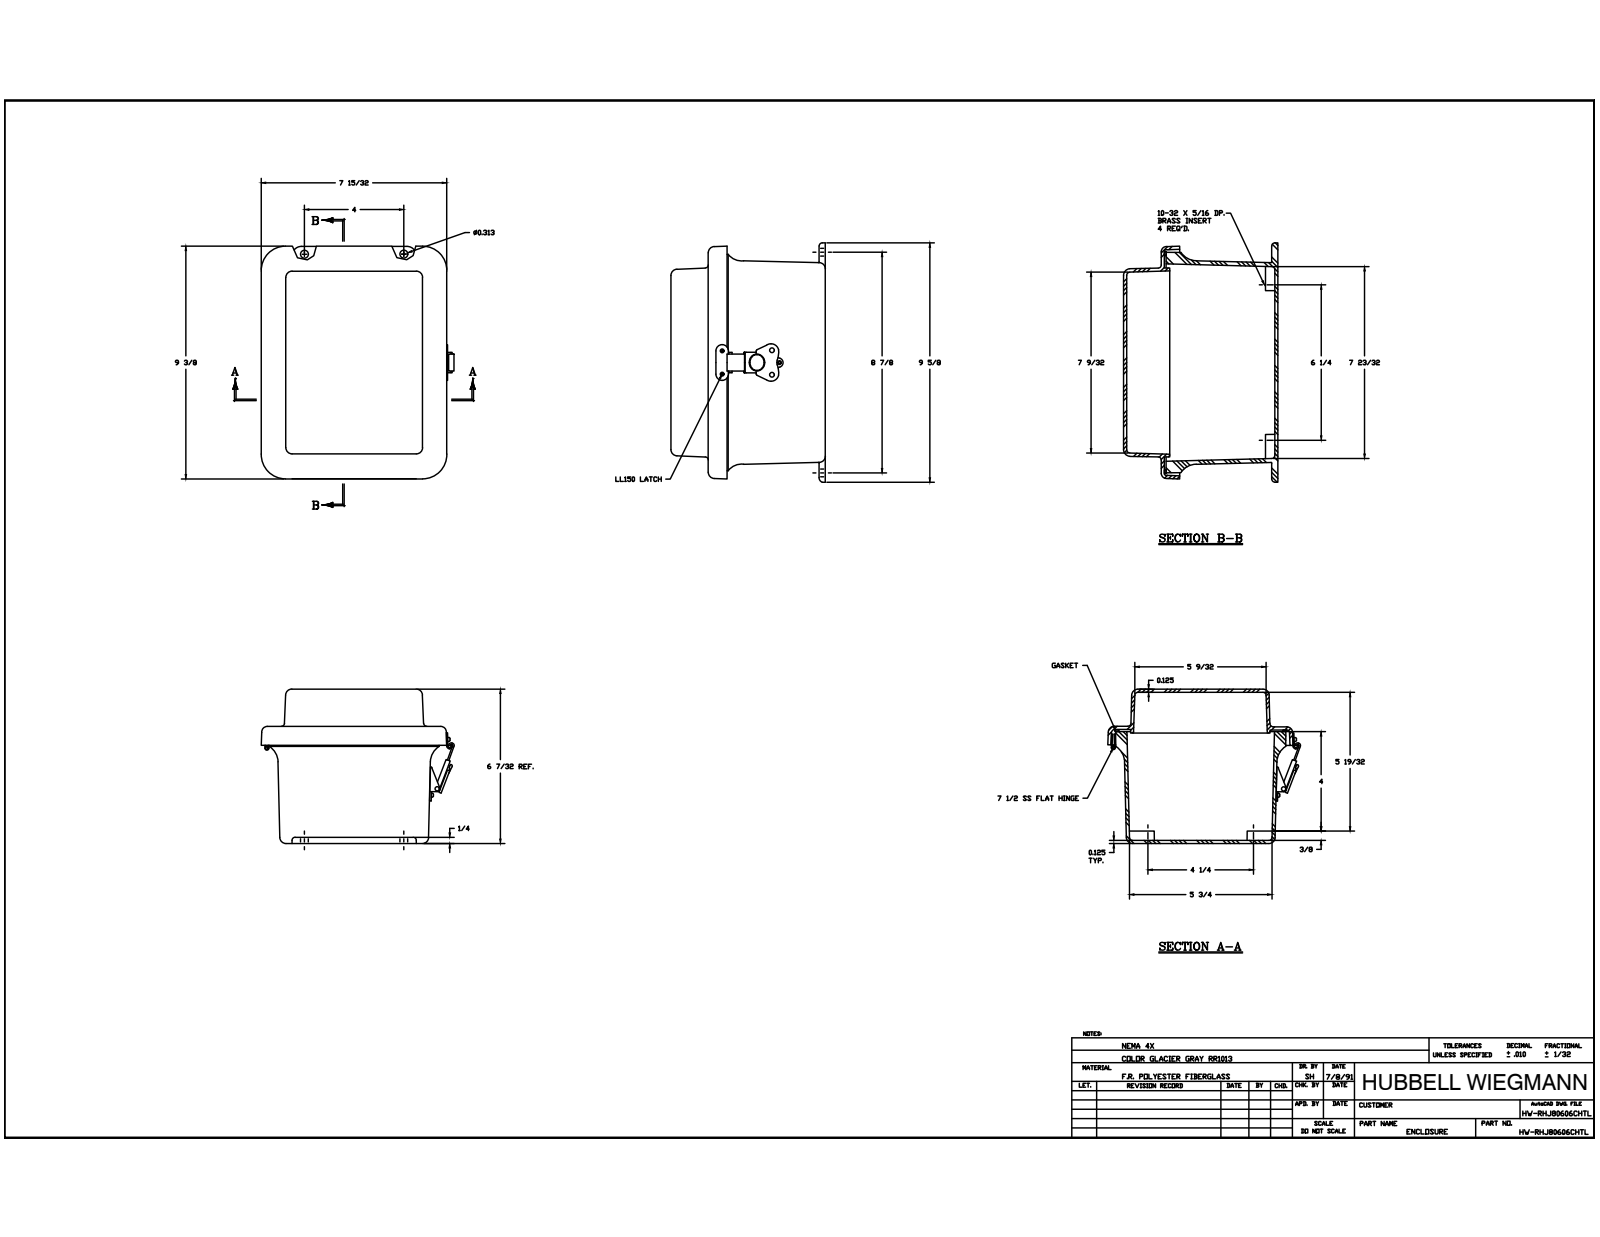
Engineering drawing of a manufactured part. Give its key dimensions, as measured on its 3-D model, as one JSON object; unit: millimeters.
{"part_name": "J806HL_4; RMINS45821P_63; RMINS45821P_64; RMINS45821P_65 (+8 more)", "step_written_by": "Autodesk Inventor 2014 (AUTOMOTIVE_DESIGN)", "units": "millimeters", "bodies": {"solids": 30, "faces": 828, "planar": 346, "cylindrical": 308, "other": 174}, "overall_size": [244.47, 192.95, 157.85], "volume_mm3": 797464, "surface_area_mm2": 443981, "round_holes": [[3.56, 10], [3.33, 6], [3.86, 5], [3.96, 4], [5.54, 4], [3.3, 2], [4.2, 2], [5, 2], [2.16, 1], [2.7, 1], [3, 1], [3.5, 1]], "round_bosses_or_shafts": [[6.35, 9], [3.17, 9], [6.86, 4], [14.8, 1], [13.3, 1], [5.3, 1], [4.7, 1], [3.94, 1]], "partial_cylinders_radius": [[0.79, 20], [3.17, 20], [6.35, 12], [2, 10], [1, 4], [1.2, 4], [5.08, 4], [7.86, 4]], "face_to_face_distances": [3.17, 3.18, 38.48, 151.5, 113.02, 154.68, 157.85, 154.67, 116.2, 41.65], "hole_center_spacings": [88.9, 33.68, 133.89, 184.12, 225.15, 6.35, 82.55, 11.92]}
